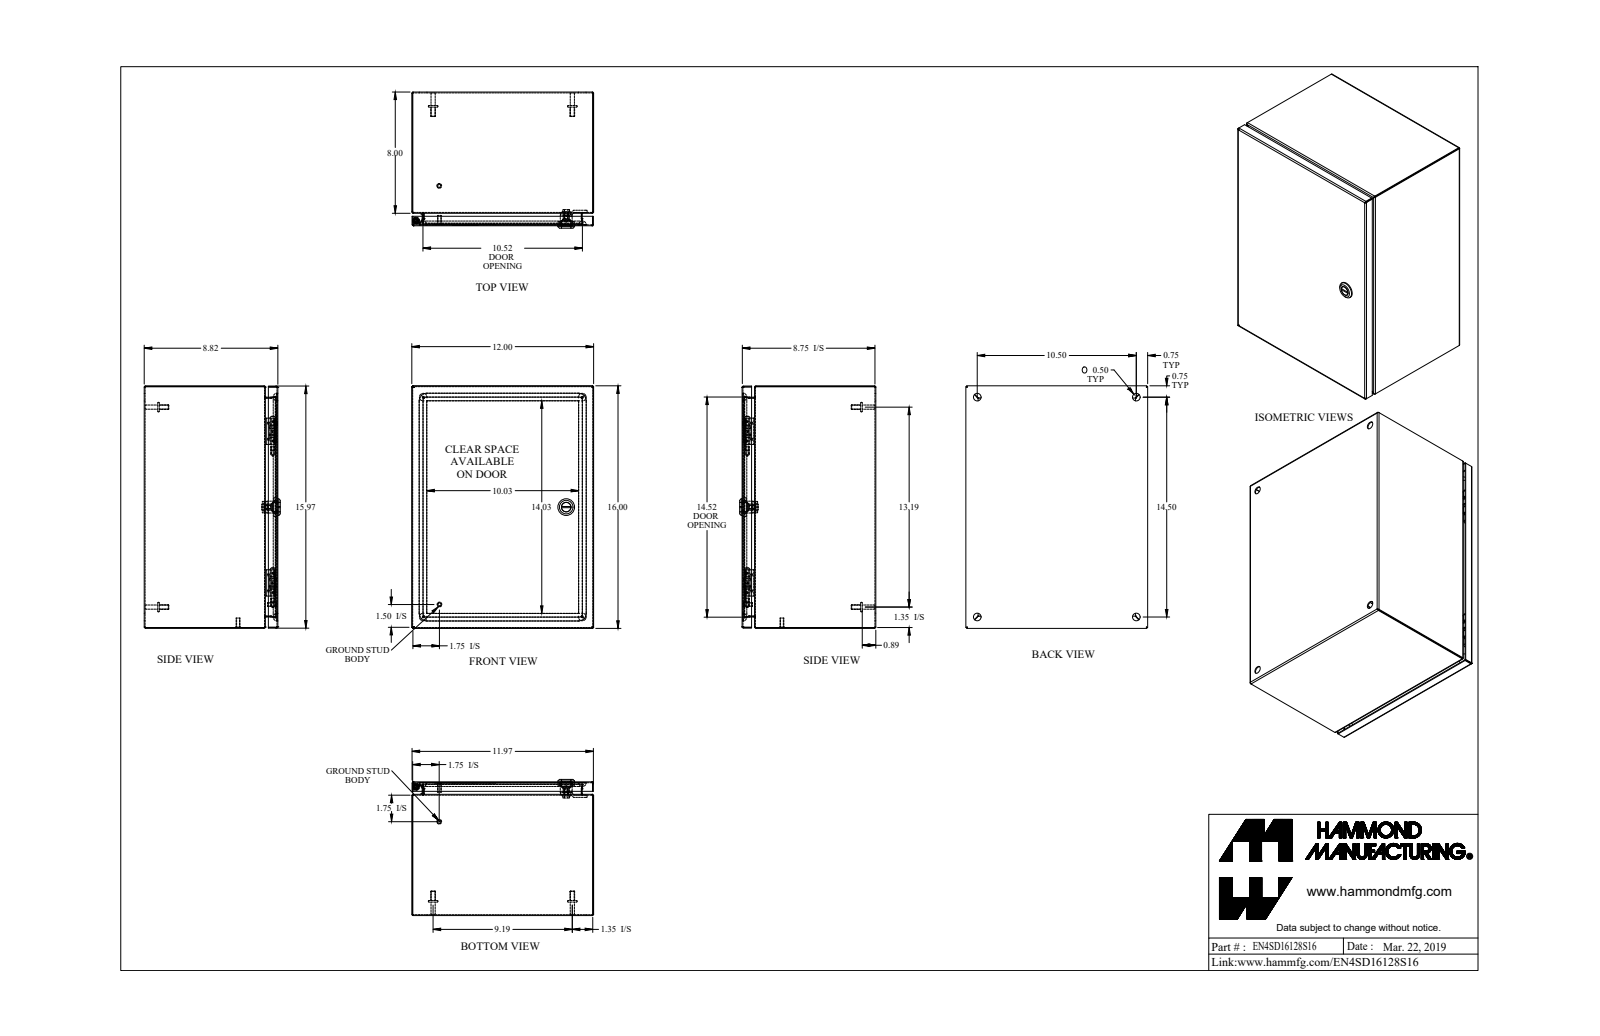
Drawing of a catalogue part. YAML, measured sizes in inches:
part_name: "EN4SD16128S16_Default"
step_written_by: "SolidWorks 2019 (CONFIG_CONTROL_DESIGN)"
units: inches
bodies: {solids: 22, faces: 657, planar: 303, cylindrical: 212, other: 142}
overall_size: [16, 12, 8.981]
volume: 59.37
surface_area: 2011
round_holes:
  - {diameter: 0.5, count: 5}
  - {diameter: 0.172, count: 1}
  - {diameter: 0.197, count: 1}
  - {diameter: 0.24, count: 1}
  - {diameter: 0.242, count: 1}
  - {diameter: 0.387, count: 1}
  - {diameter: 0.63, count: 1}
  - {diameter: 0.768, count: 1}
round_bosses_or_shafts:
  - {diameter: 0.313, count: 6}
  - {diameter: 0.625, count: 5}
  - {diameter: 0.275, count: 4}
  - {diameter: 0.25, count: 2}
  - {diameter: 1.1, count: 1}
  - {diameter: 0.785, count: 1}
  - {diameter: 0.525, count: 1}
  - {diameter: 0.475, count: 1}
partial_cylinders:
  - {radius: 0.029, count: 21}
  - {radius: 0.086, count: 21}
  - {radius: 0.188, count: 12}
  - {radius: 0.006, count: 4}
  - {radius: 0.062, count: 4}
  - {radius: 0.25, count: 4}
  - {radius: 0.499, count: 4}
  - {radius: 0.125, count: 2}
face_to_face_distances: [0.057, 11.943, 0.057, 8.707, 8.764, 8.764, 8.821, 15.943, 11.886, 12]
hole_center_spacings: [7.327, 10.5, 11.904, 14.5, 17.902]
